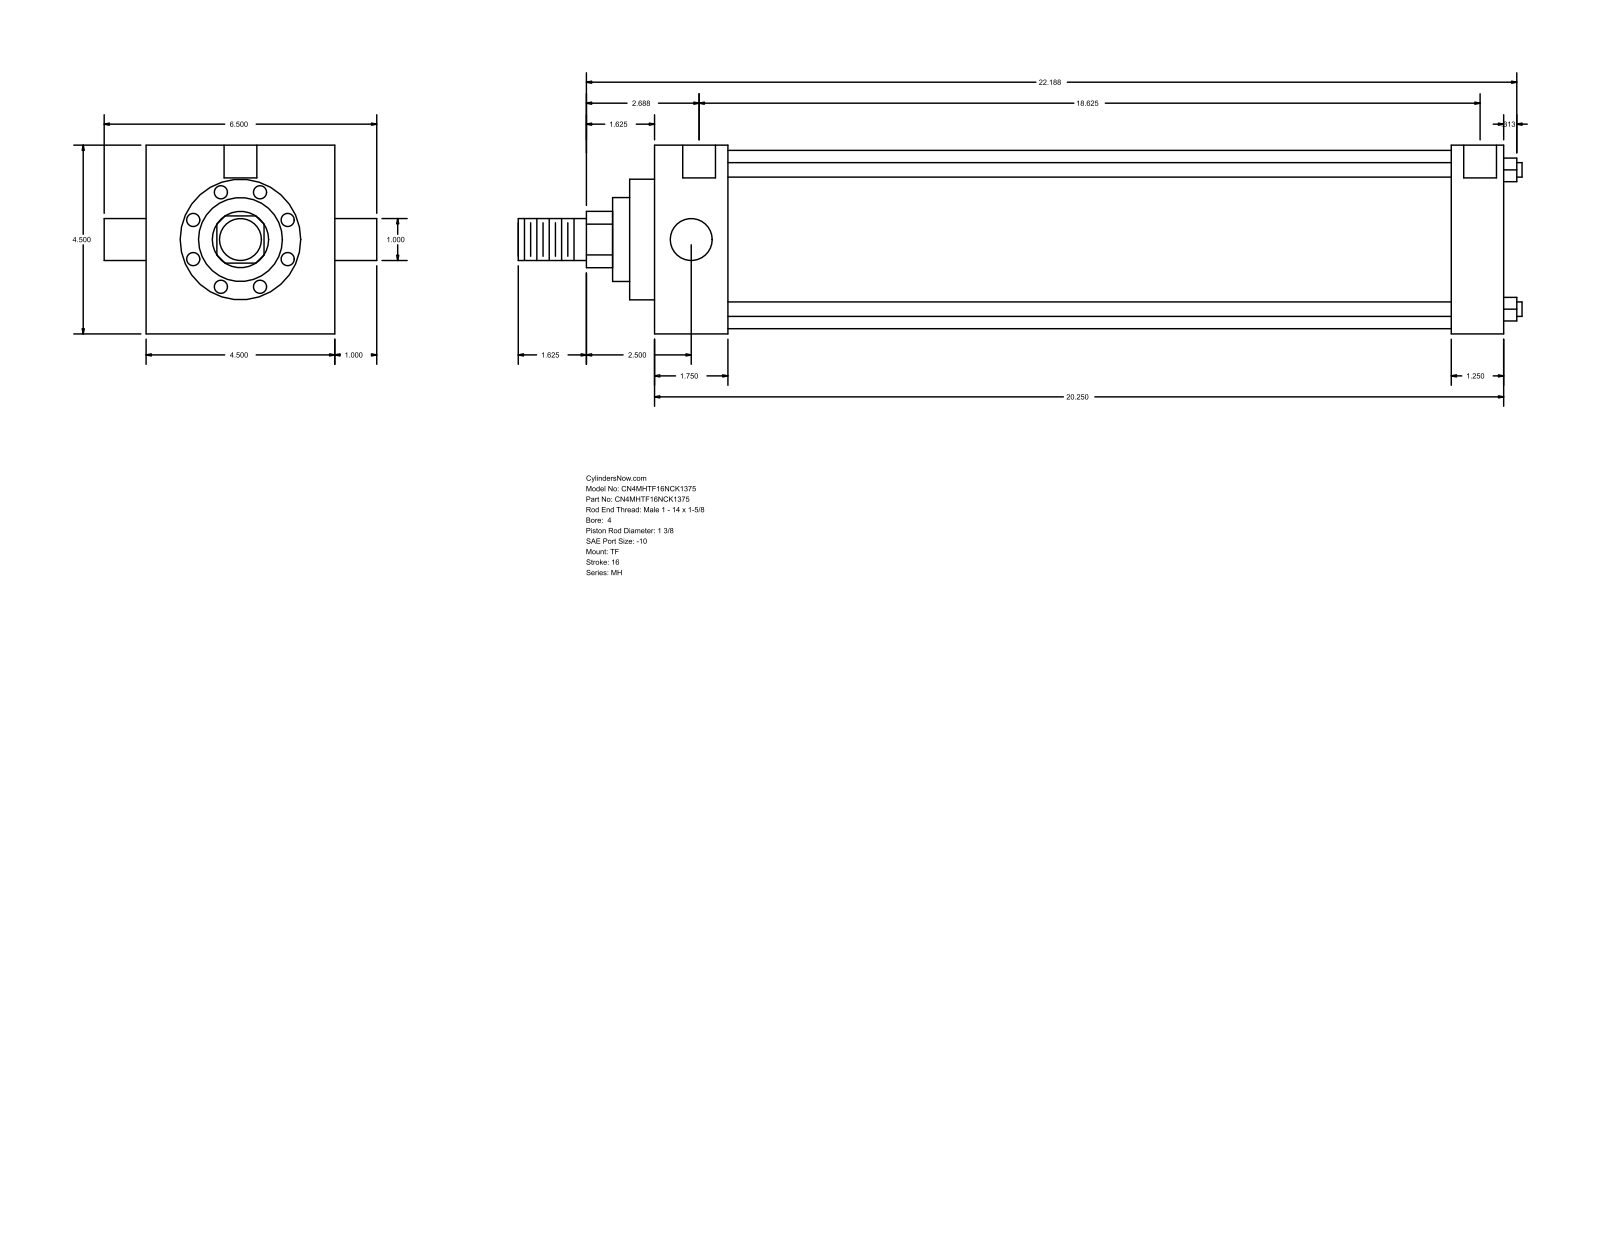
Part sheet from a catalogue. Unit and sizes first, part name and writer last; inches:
Units: inches
Overall size (bounding box): 23.937 × 6.5 × 4.5
Round holes (diameter × count): ⌀0.344 ×3, ⌀0.781 ×2
Round bosses / shafts (diameter × count): ⌀0.345 ×4, ⌀1 ×2, ⌀4.25 ×1, ⌀2.875 ×1, ⌀2 ×1, ⌀1.375 ×1
Partial cylindrical surfaces — rounded edges, fillets, slot ends (radius × count): R0.672 ×1
Main face-to-face distances: 4.5, 20.25, 1.75, 18.5, 19, 17.25, 1.25, 0.594, 2.344, 19.594
Hole centre spacings: 0.062, 0.063, 18.625, 18.687, 18.688, 18.75
Bodies: 0 solids, 86 faces (61 planar, 25 cylindrical, 0 other)
Part name (STEP PRODUCT): MH_TF__0400_1.375
STEP written by: GSSL Pune (CONFIG_CONTROL_DESIGN)
